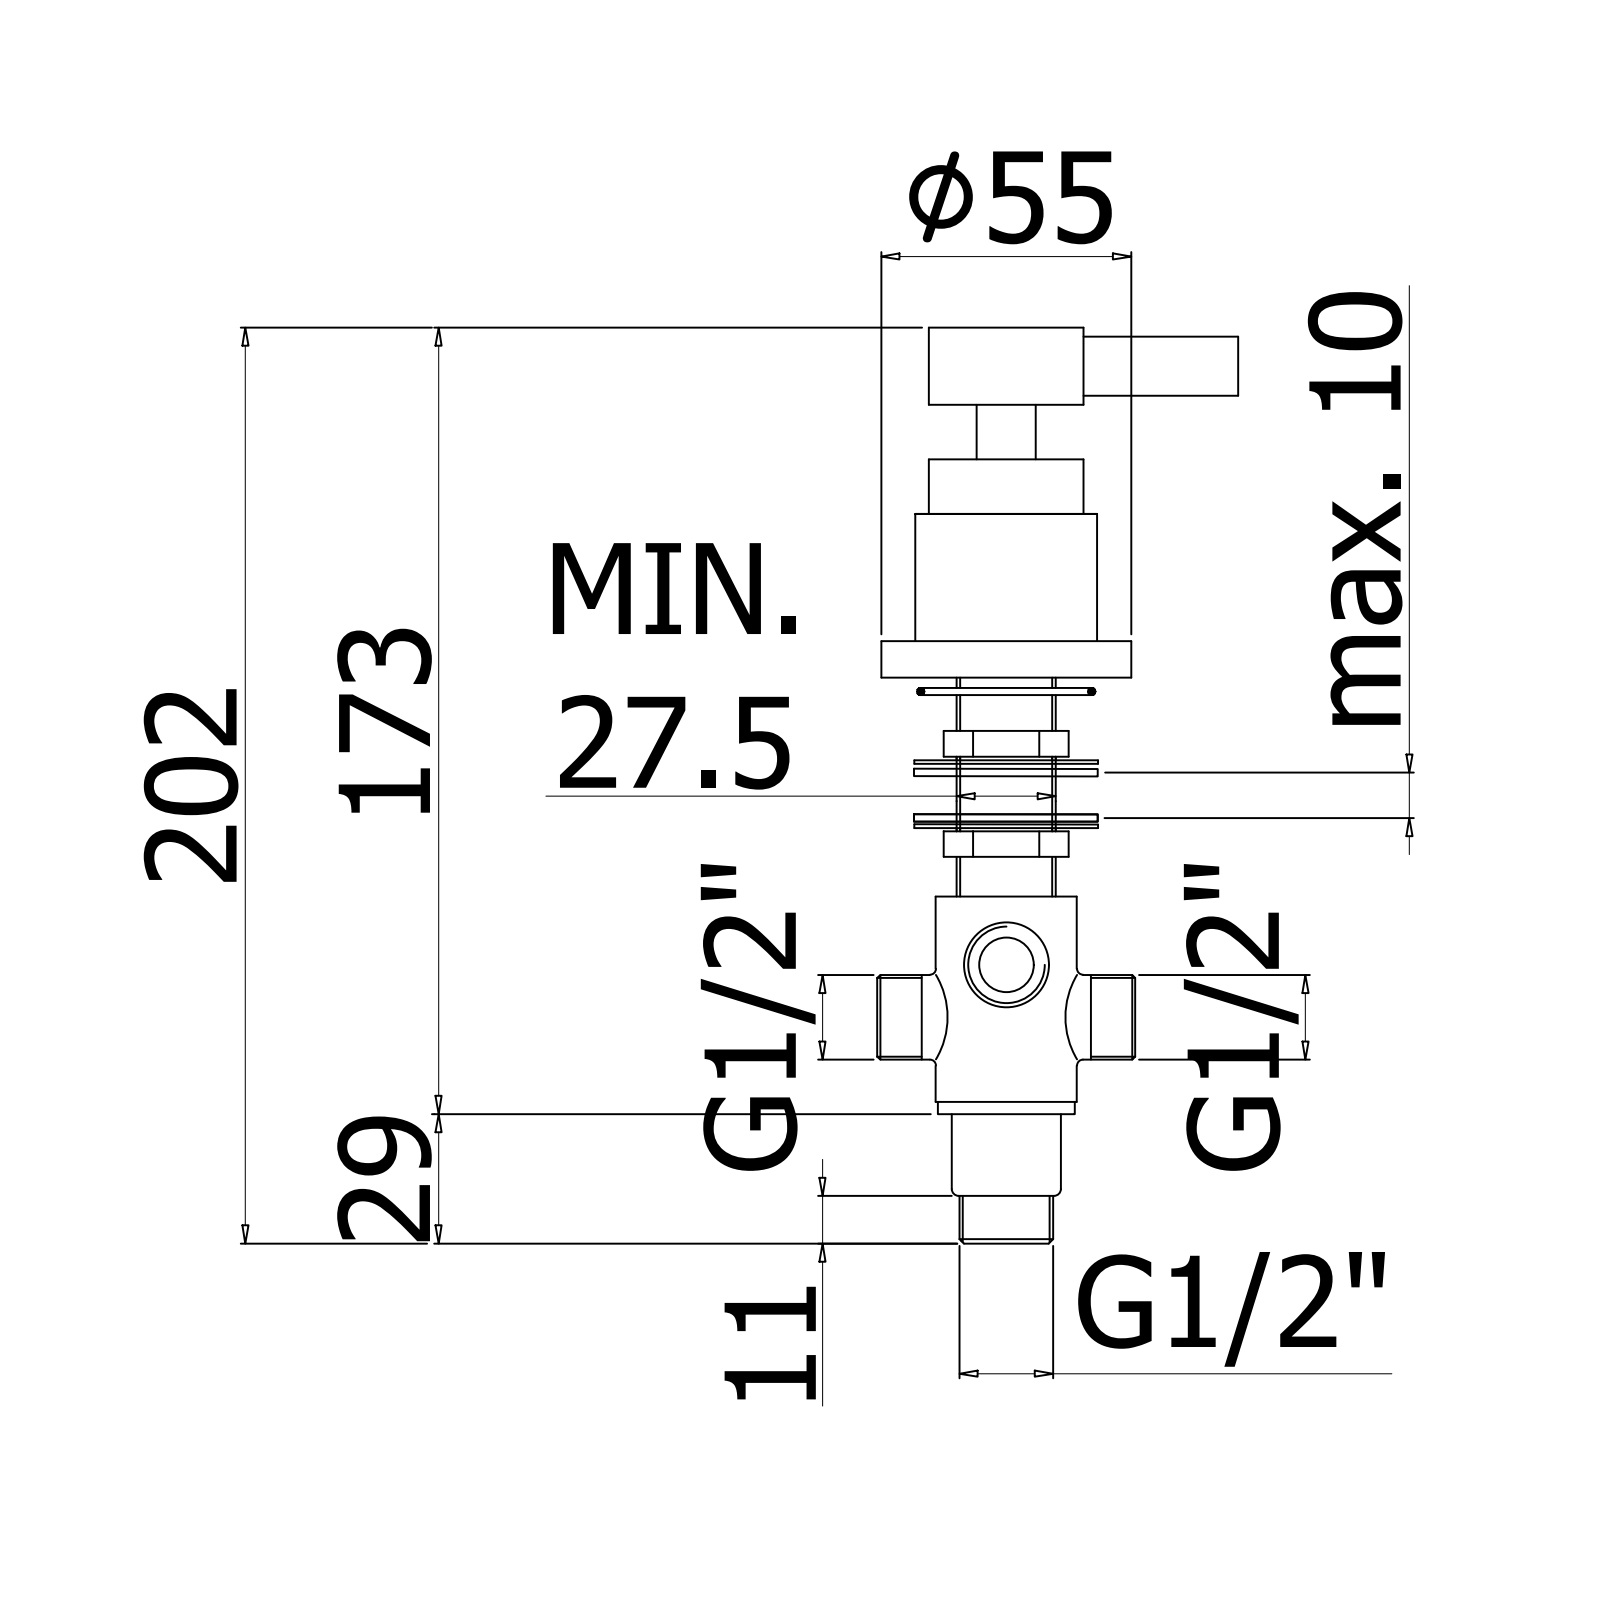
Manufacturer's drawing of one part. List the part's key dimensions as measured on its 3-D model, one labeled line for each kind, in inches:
Part name (STEP PRODUCT): ZDEV082CR
STEP written by: CREO PARAMETRIC BY PTC INC, 2020044 (CONFIG_CONTROL_DESIGN)
Units: inches
Bodies: 5 solids, 172 faces (96 planar, 44 cylindrical, 32 other)
Overall size (bounding box): 3.063 × 2.76 × 2.165
Volume: 3.659 in³ · Surface area: 38.65 in²
Round holes (diameter × count): ⌀0.197 ×1, ⌀0.307 ×1, ⌀0.531 ×1, ⌀0.787 ×1, ⌀1.012 ×1, ⌀1.122 ×1, ⌀1.437 ×1, ⌀1.85 ×1, ⌀2.087 ×1
Round bosses / shafts (diameter × count): ⌀0.512 ×2, ⌀2.165 ×1, ⌀1.929 ×1, ⌀1.567 ×1, ⌀1.417 ×1, ⌀1.339 ×1, ⌀1.22 ×1, ⌀0.354 ×1
Partial cylindrical surfaces — rounded edges, fillets, slot ends (radius × count): R0.118 ×1
Main face-to-face distances: 1.752, 0.236, 1.516, 0.197, 2.807, 2.571, 1.055, 1.902, 2.138, 0.386
